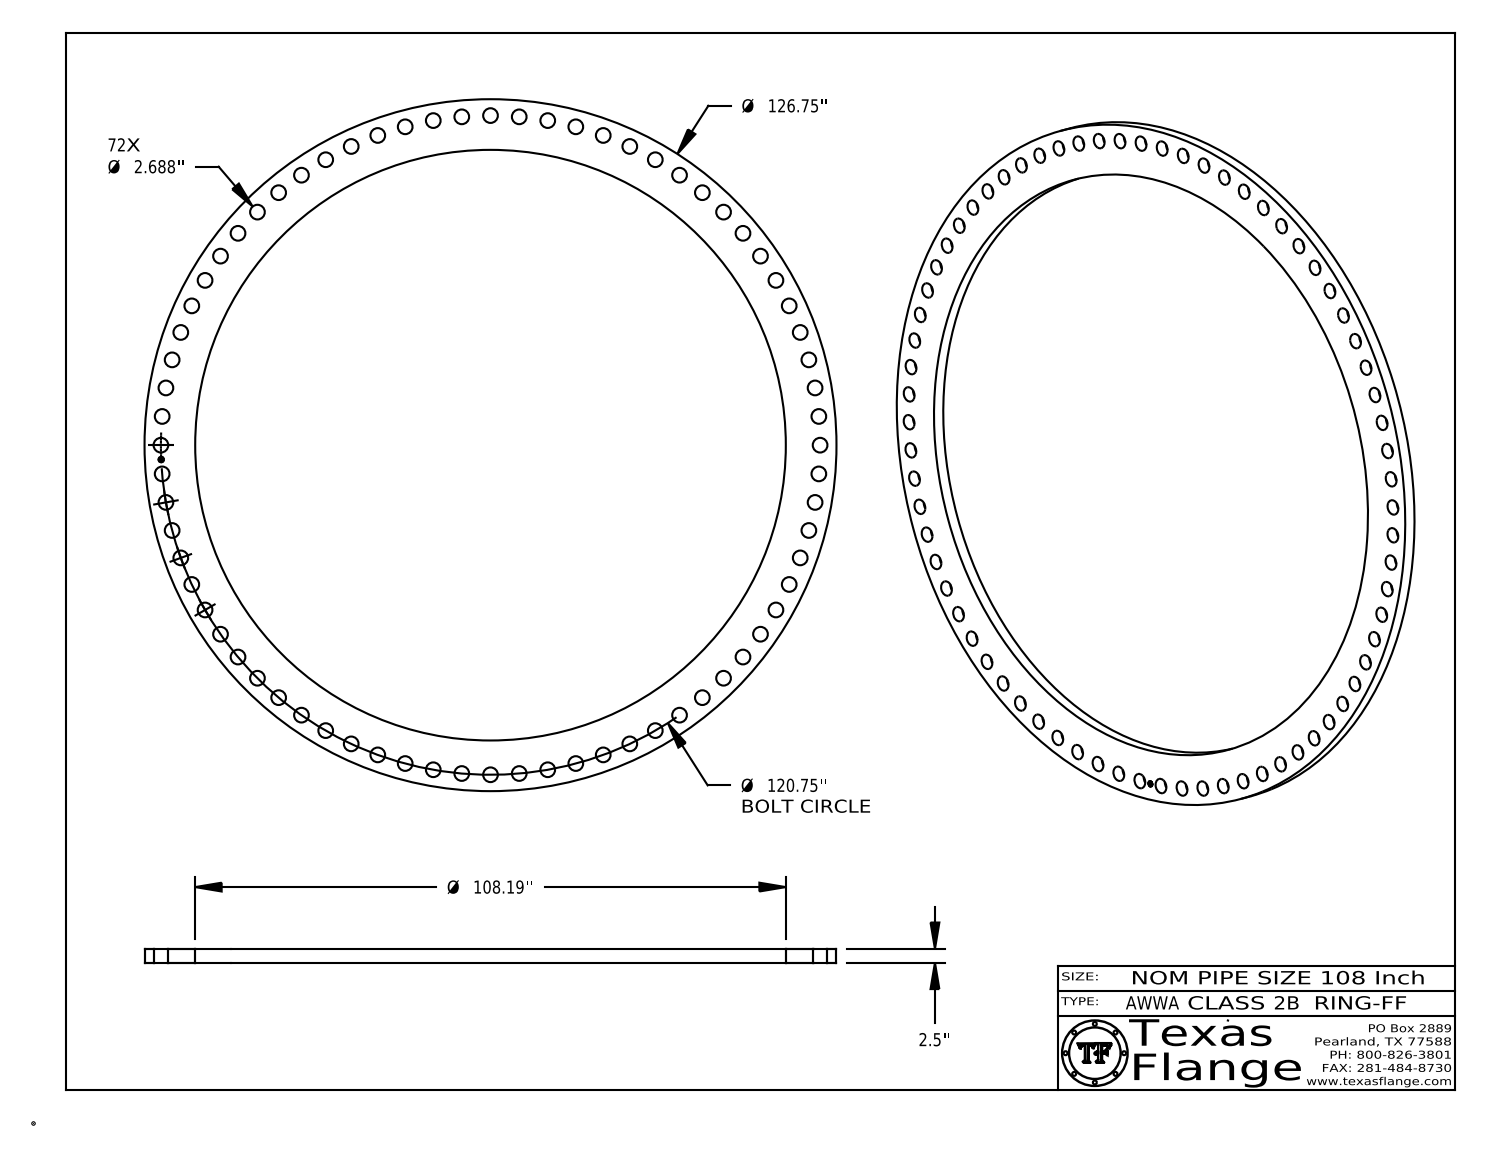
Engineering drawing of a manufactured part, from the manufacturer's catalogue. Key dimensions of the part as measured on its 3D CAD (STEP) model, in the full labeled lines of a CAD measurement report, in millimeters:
Part name (STEP PRODUCT): AWWA Class 2B-RING-FF
STEP written by: CATIA V5 STEP AP214 (AUTOMOTIVE_DESIGN)
Units: millimetres
Bodies: 1 solid, 535 faces (367 planar, 168 cylindrical, 0 other)
Overall size (bounding box): 3219.5 × 3219.5 × 63.5
Volume: 123 600 000 mm³ · Surface area: 6 063 000 mm²
Round holes (diameter × count): ⌀68.3 ×72, ⌀25.4 ×1, ⌀2748 ×1
Round bosses / shafts (diameter × count): ⌀1.5 ×8, ⌀3219.5 ×1, ⌀20 ×1
Main face-to-face distances: 63.5, 0.4, 63.1, 7.6, 7.4, 1.4, 4.9, 6.3, 1.1, 3.8
Hole centre spacings: 1533.5, 267.3, 133.8, 1533.5, 793.8, 532.6, 663.8, 1049
